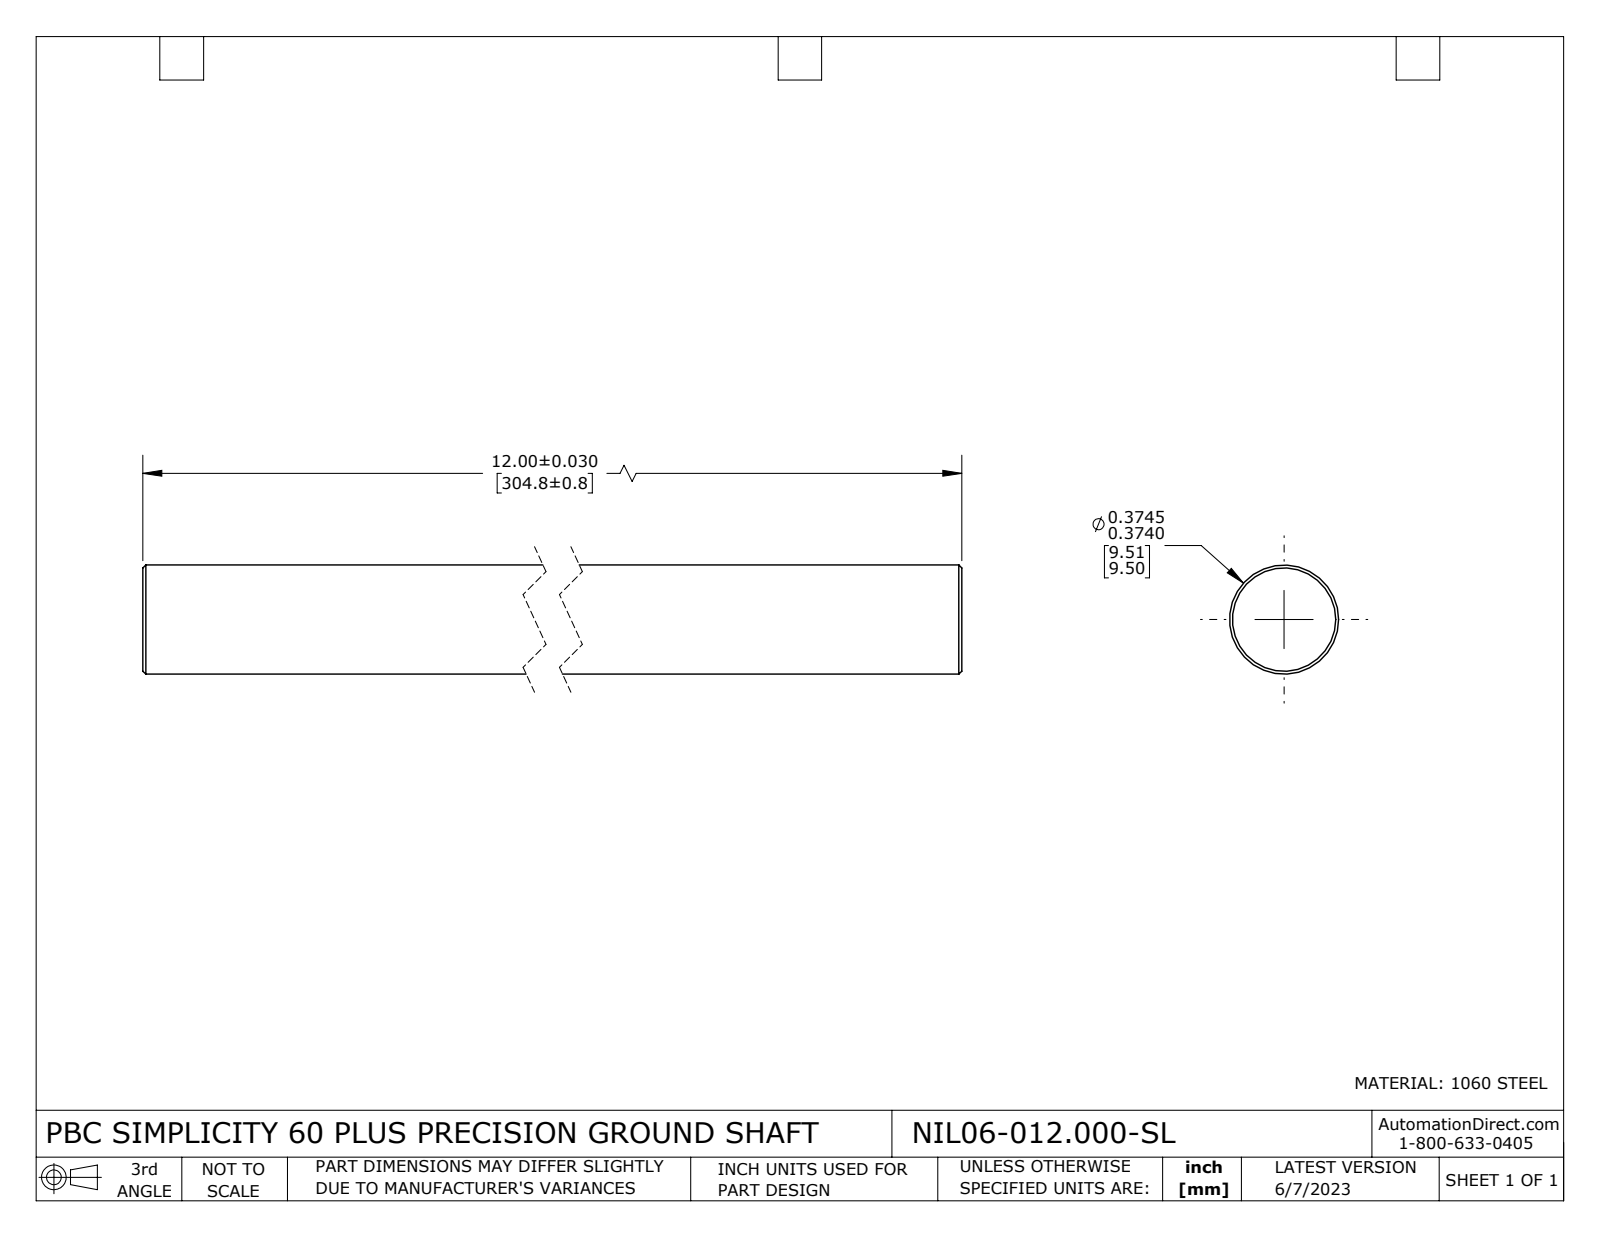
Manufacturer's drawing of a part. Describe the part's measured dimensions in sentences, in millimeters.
The part is named "NIL06-012.000-SL". Its 3-D file was written by "SolidWorks 2021 (CONFIG_CONTROL_DESIGN)". It is 1 solid with 8 faces: 2 planar, 2 cylindrical and 4 other. Overall it measures 304.8 by 9.5 by 9.5 millimeters. Its volume is 21 710 cubic millimeters and its surface area 9 252 square millimeters. Round bosses or shafts: 1 of diameter 9.5. The main face-to-face distances are 304.8.
